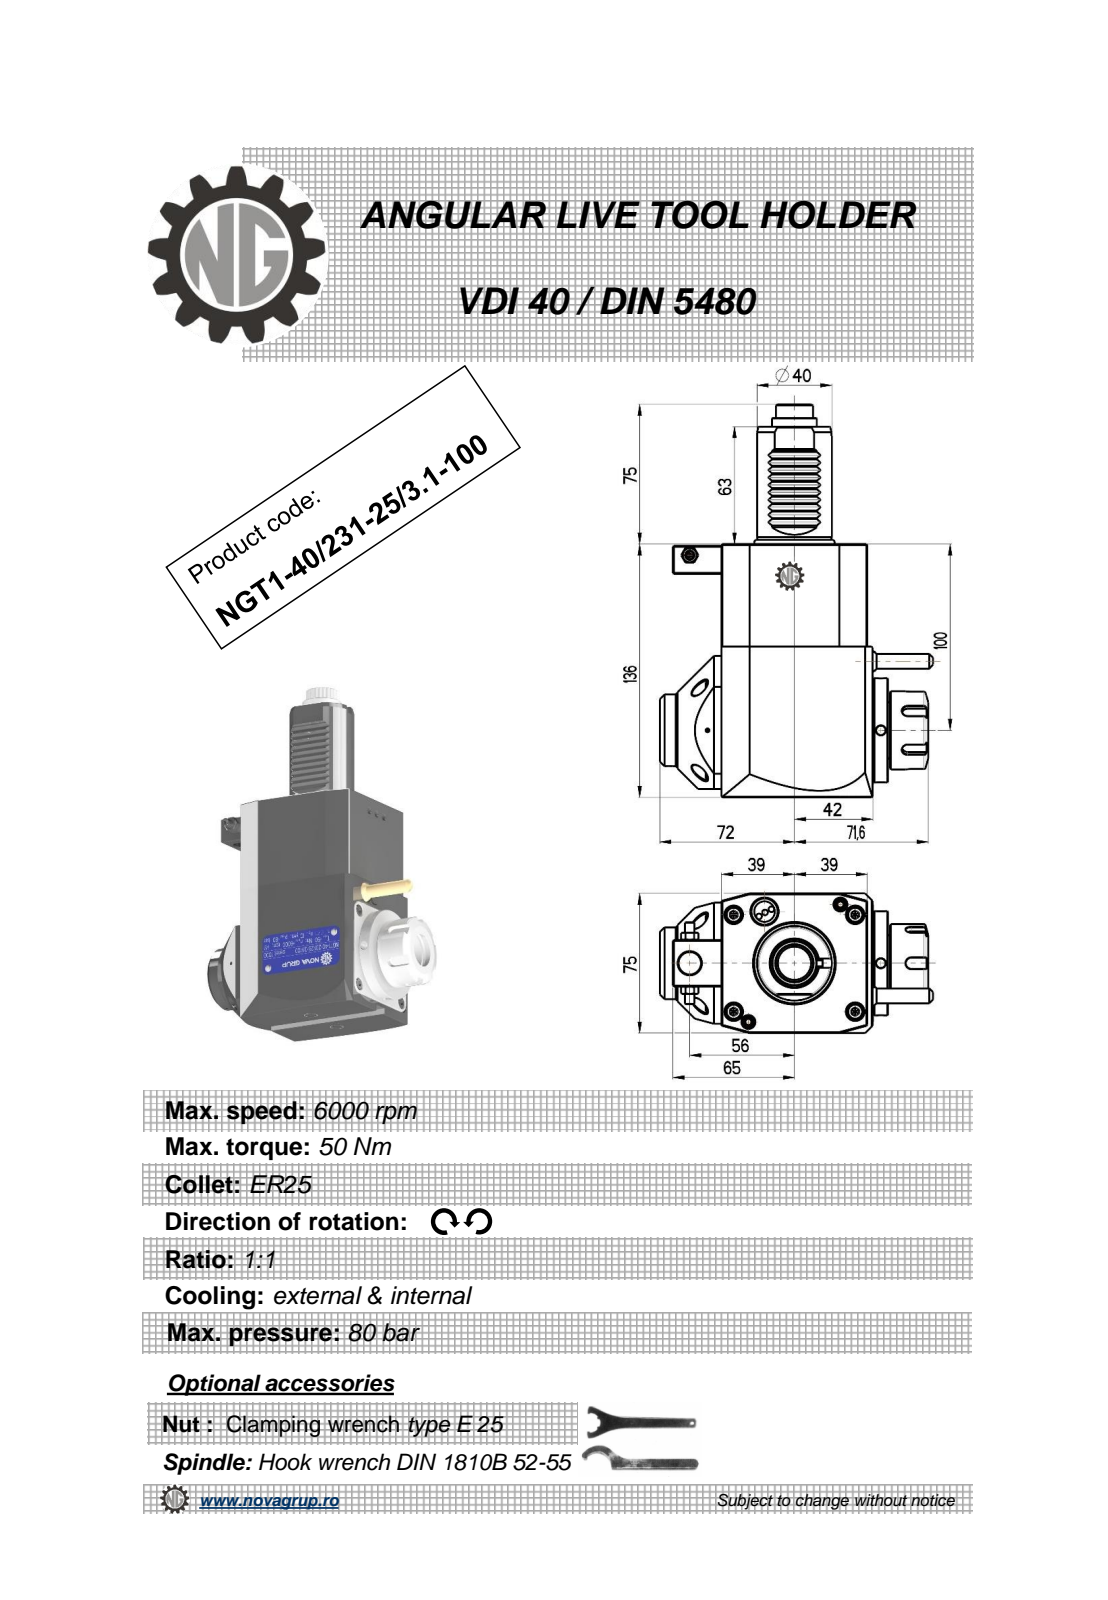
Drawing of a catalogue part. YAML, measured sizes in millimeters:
part_name: "NGT1_40_231_25_3_1_100"
step_written_by: "PRO/ENGINEER BY PARAMETRIC TECHNOLOGY CORPORATION, 2010280 (CONFIG_CONTROL_DESIGN)"
units: millimeters
bodies: {solids: 1, faces: 549, planar: 193, cylindrical: 183, other: 173}
overall_size: [211, 146.14, 75]
volume: 1012000
surface_area: 78017
round_holes:
  - {diameter: 5, count: 3}
  - {diameter: 3, count: 1}
  - {diameter: 4.2, count: 1}
  - {diameter: 9.5, count: 1}
  - {diameter: 12, count: 1}
  - {diameter: 20.3, count: 1}
round_bosses_or_shafts:
  - {diameter: 56, count: 1}
  - {diameter: 43, count: 1}
  - {diameter: 42, count: 1}
  - {diameter: 40, count: 1}
  - {diameter: 38.5, count: 1}
  - {diameter: 33, count: 1}
  - {diameter: 24, count: 1}
  - {diameter: 11.2, count: 1}
partial_cylinders:
  - {radius: 2.08, count: 48}
  - {radius: 0.26, count: 12}
  - {radius: 0.3, count: 10}
  - {radius: 0.22, count: 6}
  - {radius: 3, count: 5}
  - {radius: 9.08, count: 1}
  - {radius: 9.92, count: 1}
  - {radius: 15, count: 1}
face_to_face_distances: [75, 136, 78, 81, 3, 11, 8, 84.88, 7.5, 80.8]
hole_center_spacings: [40.93, 57.24, 91.5, 102.25, 138.89]
